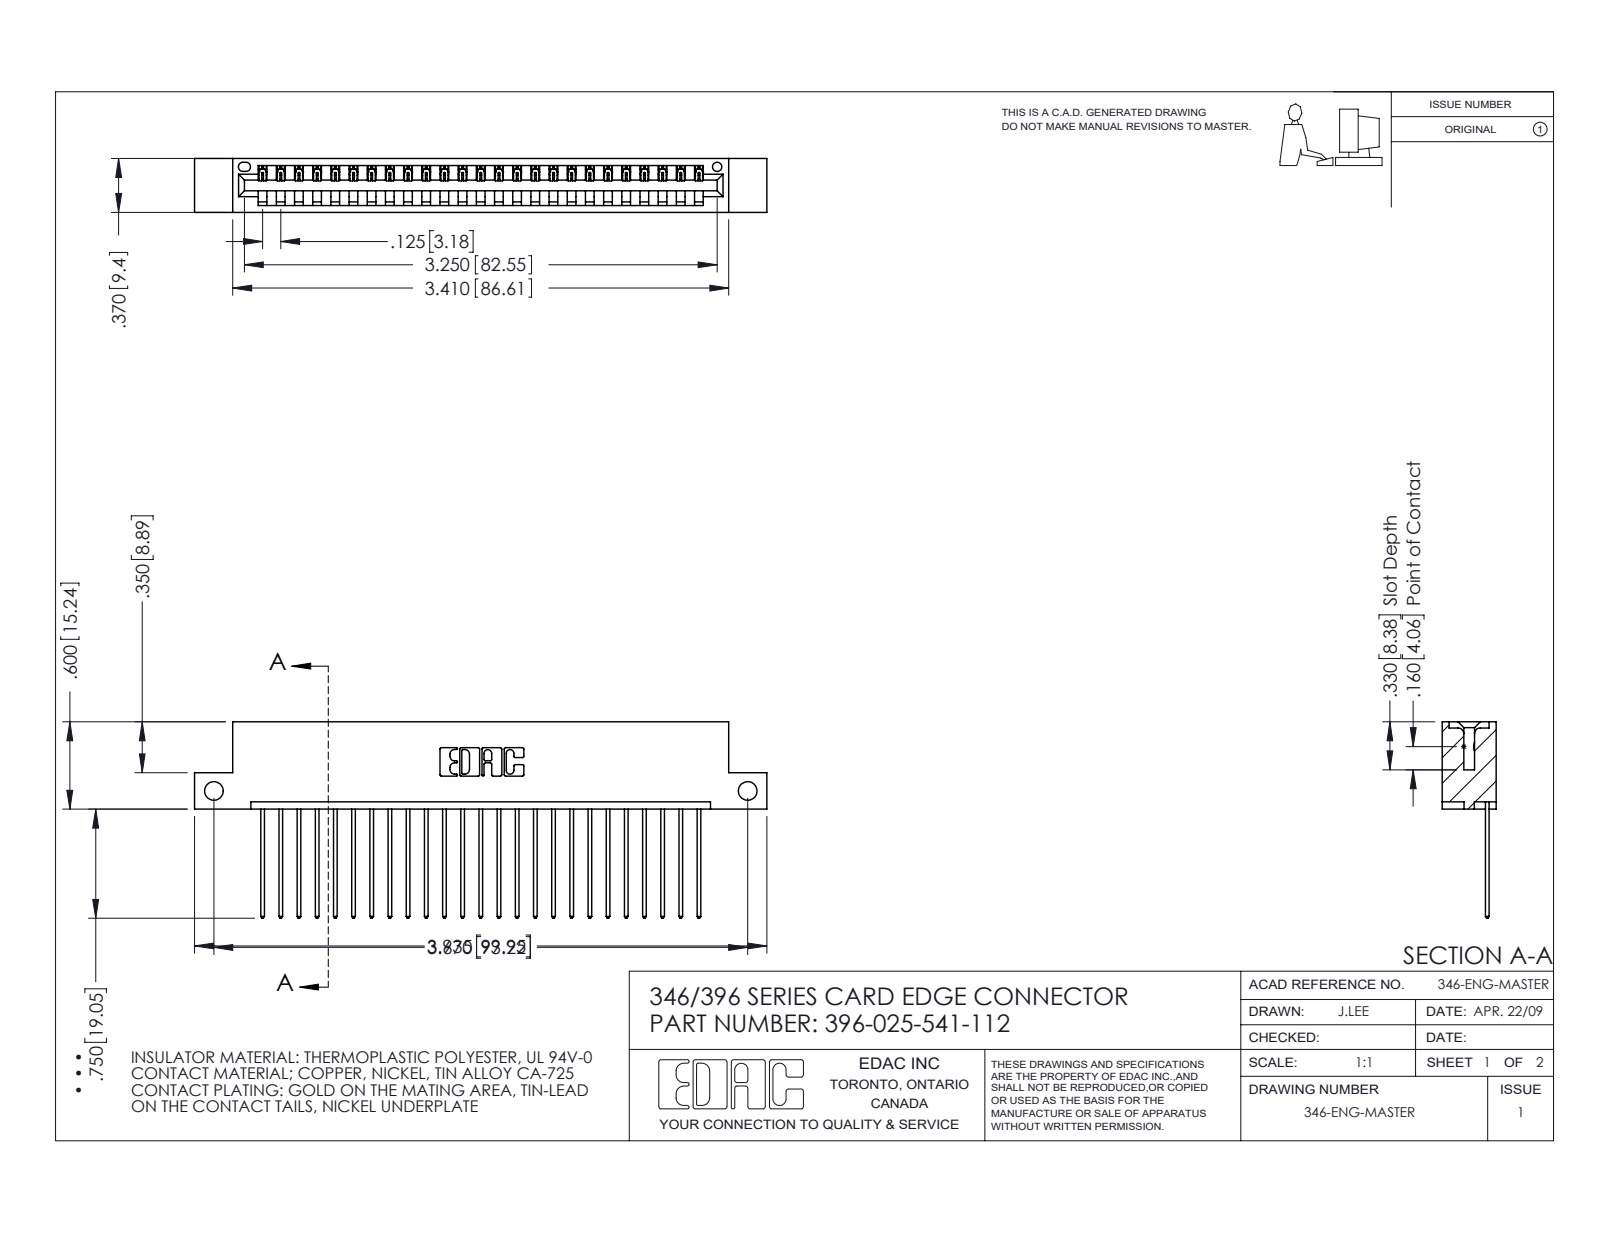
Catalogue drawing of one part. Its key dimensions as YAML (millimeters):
part_name: "345-292-001_345-293-141; 346 Part_Flush Mounting Lugs - Side Mount; 396-025-541-112"
step_written_by: "SolidWorks 2016 (CONFIG_CONTROL_DESIGN)"
units: millimeters
bodies: {solids: 26, faces: 1572, planar: 1076, cylindrical: 496, other: 0}
overall_size: [99.9, 34.3, 9.4]
volume: 9440
surface_area: 11970
round_holes:
  - {diameter: 3.3, count: 2}
  - {diameter: 1.6, count: 1}
partial_cylinders:
  - {radius: 0.2, count: 50}
  - {radius: 0.3, count: 50}
  - {radius: 0.3, count: 22}
  - {radius: 0.2, count: 6}
  - {radius: 0.8, count: 6}
  - {radius: 0.7, count: 3}
  - {radius: 0.8, count: 2}
  - {radius: 1, count: 2}
face_to_face_distances: [1.2, 8.2, 6.4, 9.4, 1.8, 7.6, 0.6, 3.8, 5.6, 2.5]
hole_center_spacings: [93.2]
